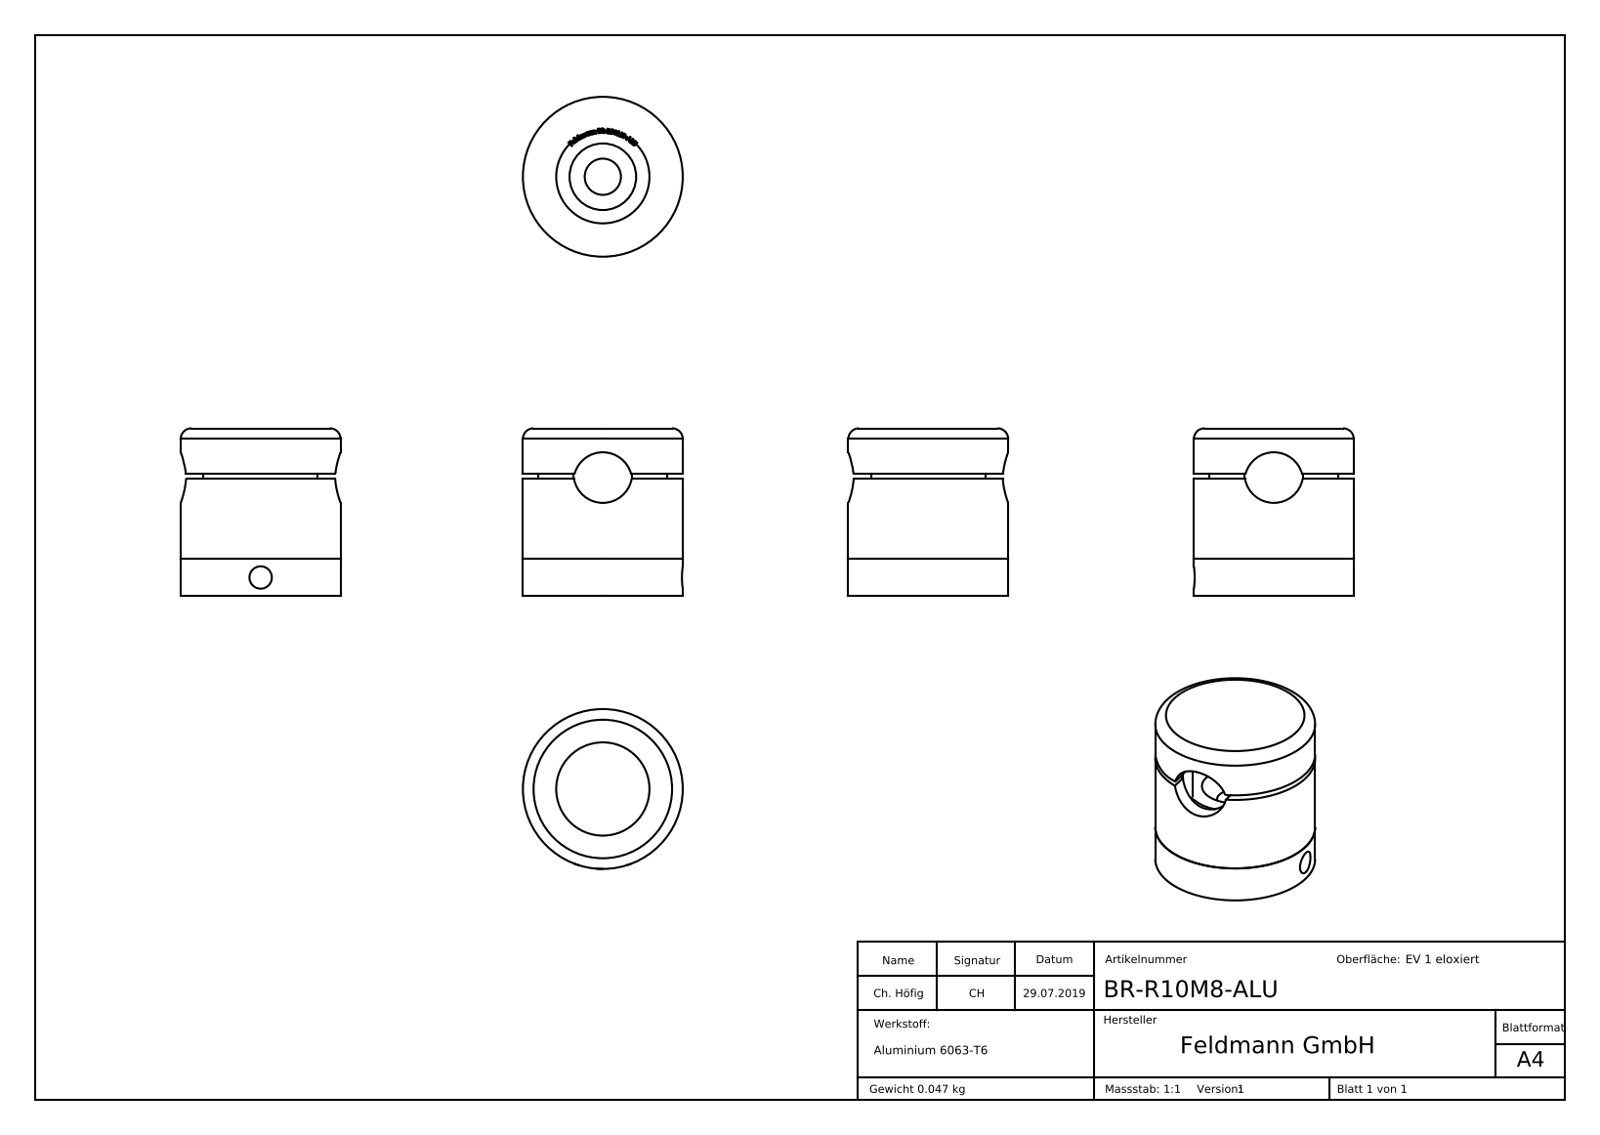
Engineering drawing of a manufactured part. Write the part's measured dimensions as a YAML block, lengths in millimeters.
part_name: "BR-R1XM8-XXX Teil1; BR-R1XM8-XXX Teil2; BR-R10M8-ALU; BR-R1XM8-XXX Teil1_BR-1XM8-ALU Teil1 (+3 more)"
step_written_by: "SolidWorks 2015 (CONFIG_CONTROL_DESIGN)"
units: millimeters
bodies: {solids: 3, faces: 322, planar: 185, cylindrical: 15, other: 122}
overall_size: [64.34, 30, 30]
volume: 17288
surface_area: 9596
round_holes:
  - {diameter: 4.2, count: 1}
  - {diameter: 6.8, count: 1}
  - {diameter: 12.5, count: 1}
  - {diameter: 24.2, count: 1}
round_bosses_or_shafts:
  - {diameter: 30, count: 1}
  - {diameter: 20, count: 1}
partial_cylinders:
  - {radius: 5.5, count: 2}
  - {radius: 8.75, count: 1}
  - {radius: 12.05, count: 1}
face_to_face_distances: [7, 31.5, 24.5, 16, 8.5, 23, 15.5, 22, 15, 1]
